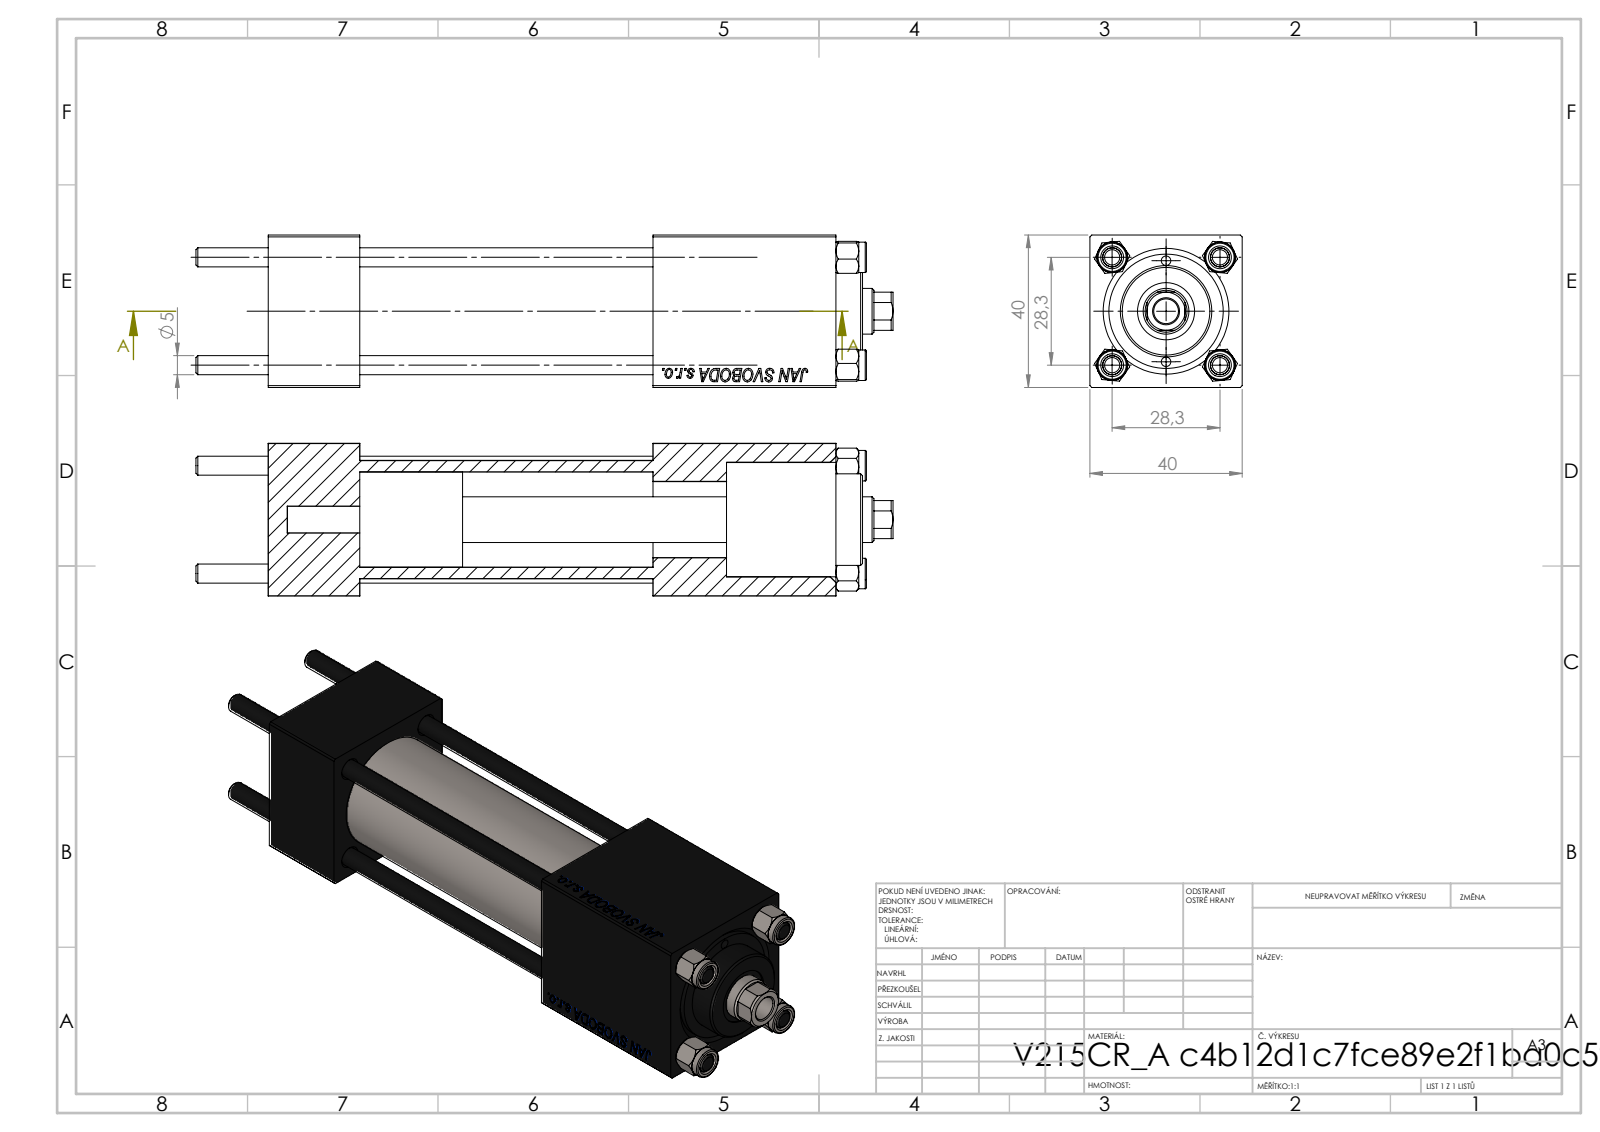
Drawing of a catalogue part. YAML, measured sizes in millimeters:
part_name: "V215CR_BODY_A; CR025_012_A_0_G_A_G_M_020_+#_##_TYCINKA; V215_VC_A; NUT_M5 (+1 more)"
step_written_by: "SolidWorks 2019 (CONFIG_CONTROL_DESIGN)"
units: millimeters
bodies: {solids: 11, faces: 1137, planar: 519, cylindrical: 82, other: 536}
overall_size: [183, 40, 40]
volume: 158441
surface_area: 67244
round_holes:
  - {diameter: 5, count: 4}
  - {diameter: 20, count: 3}
  - {diameter: 2.5, count: 2}
  - {diameter: 7, count: 2}
  - {diameter: 13.16, count: 2}
  - {diameter: 6.5, count: 1}
  - {diameter: 12, count: 1}
  - {diameter: 15, count: 1}
  - {diameter: 25, count: 1}
  - {diameter: 30, count: 1}
round_bosses_or_shafts:
  - {diameter: 8, count: 4}
  - {diameter: 31, count: 1}
  - {diameter: 24, count: 1}
partial_cylinders:
  - {radius: 5.5, count: 1}
face_to_face_distances: [40, 24, 120.3, 96.3, 149, 125, 28.7, 101, 77, 19.3]
hole_center_spacings: [14.18, 20.01, 28.3, 30.84, 13.25, 40.02, 26.5, 102]
